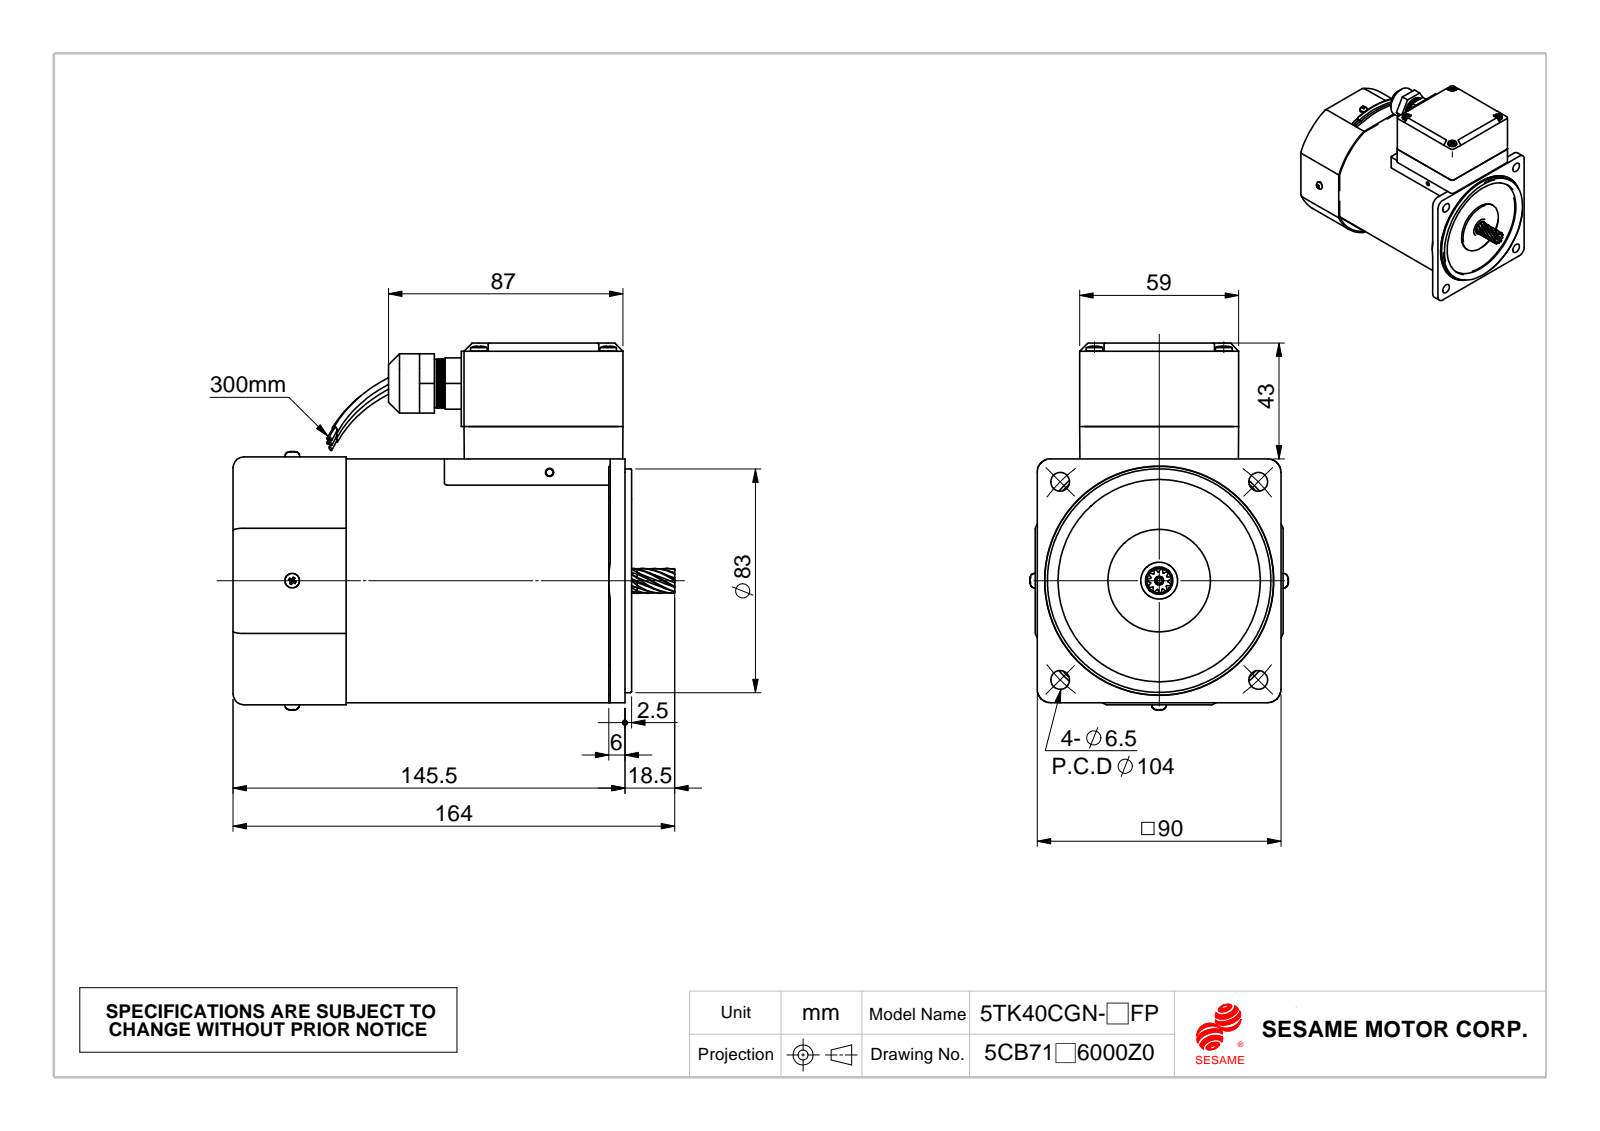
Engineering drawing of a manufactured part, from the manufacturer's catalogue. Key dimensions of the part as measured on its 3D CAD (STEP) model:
Part name (STEP PRODUCT): Ts下墊片; M590Ts-F; 風扇蓋FC-9042-21; 成品180度
STEP written by: SolidWorks 2010 (CONFIG_CONTROL_DESIGN)
Units: millimetres
Bodies: 19 solids, 2785 faces (343 planar, 947 cylindrical, 1495 other)
Overall size (bounding box): 164 × 136.21 × 95.92
Volume: 1 031 000 mm³ · Surface area: 148 972 mm²
Round holes (diameter × count): ⌀3.3 ×4, ⌀3.5 ×4, ⌀3.9 ×4, ⌀4.3 ×4, ⌀7 ×4, ⌀2.5 ×3, ⌀2 ×1, ⌀6.5 ×1, ⌀11 ×1, ⌀12 ×1, ⌀13.7 ×1, ⌀14.5 ×1
Round bosses / shafts (diameter × count): ⌀3 ×6, ⌀6.3 ×4, ⌀11 ×3, ⌀5.5 ×2, ⌀90.5 ×1, ⌀86 ×1, ⌀85 ×1, ⌀84 ×1
Partial cylindrical surfaces — rounded edges, fillets, slot ends (radius × count): R0.3 ×16, R2 ×16, R1 ×10, R4 ×10, R0.5 ×8, R3 ×8, R1.5 ×4, R1.75 ×4
Main face-to-face distances: 1, 12, 0.75, 91, 3.9, 16, 140, 143.9, 139, 142.9
Hole centre spacings: 48, 52, 73.54, 11.67, 12.35, 12.7, 24.93, 25
